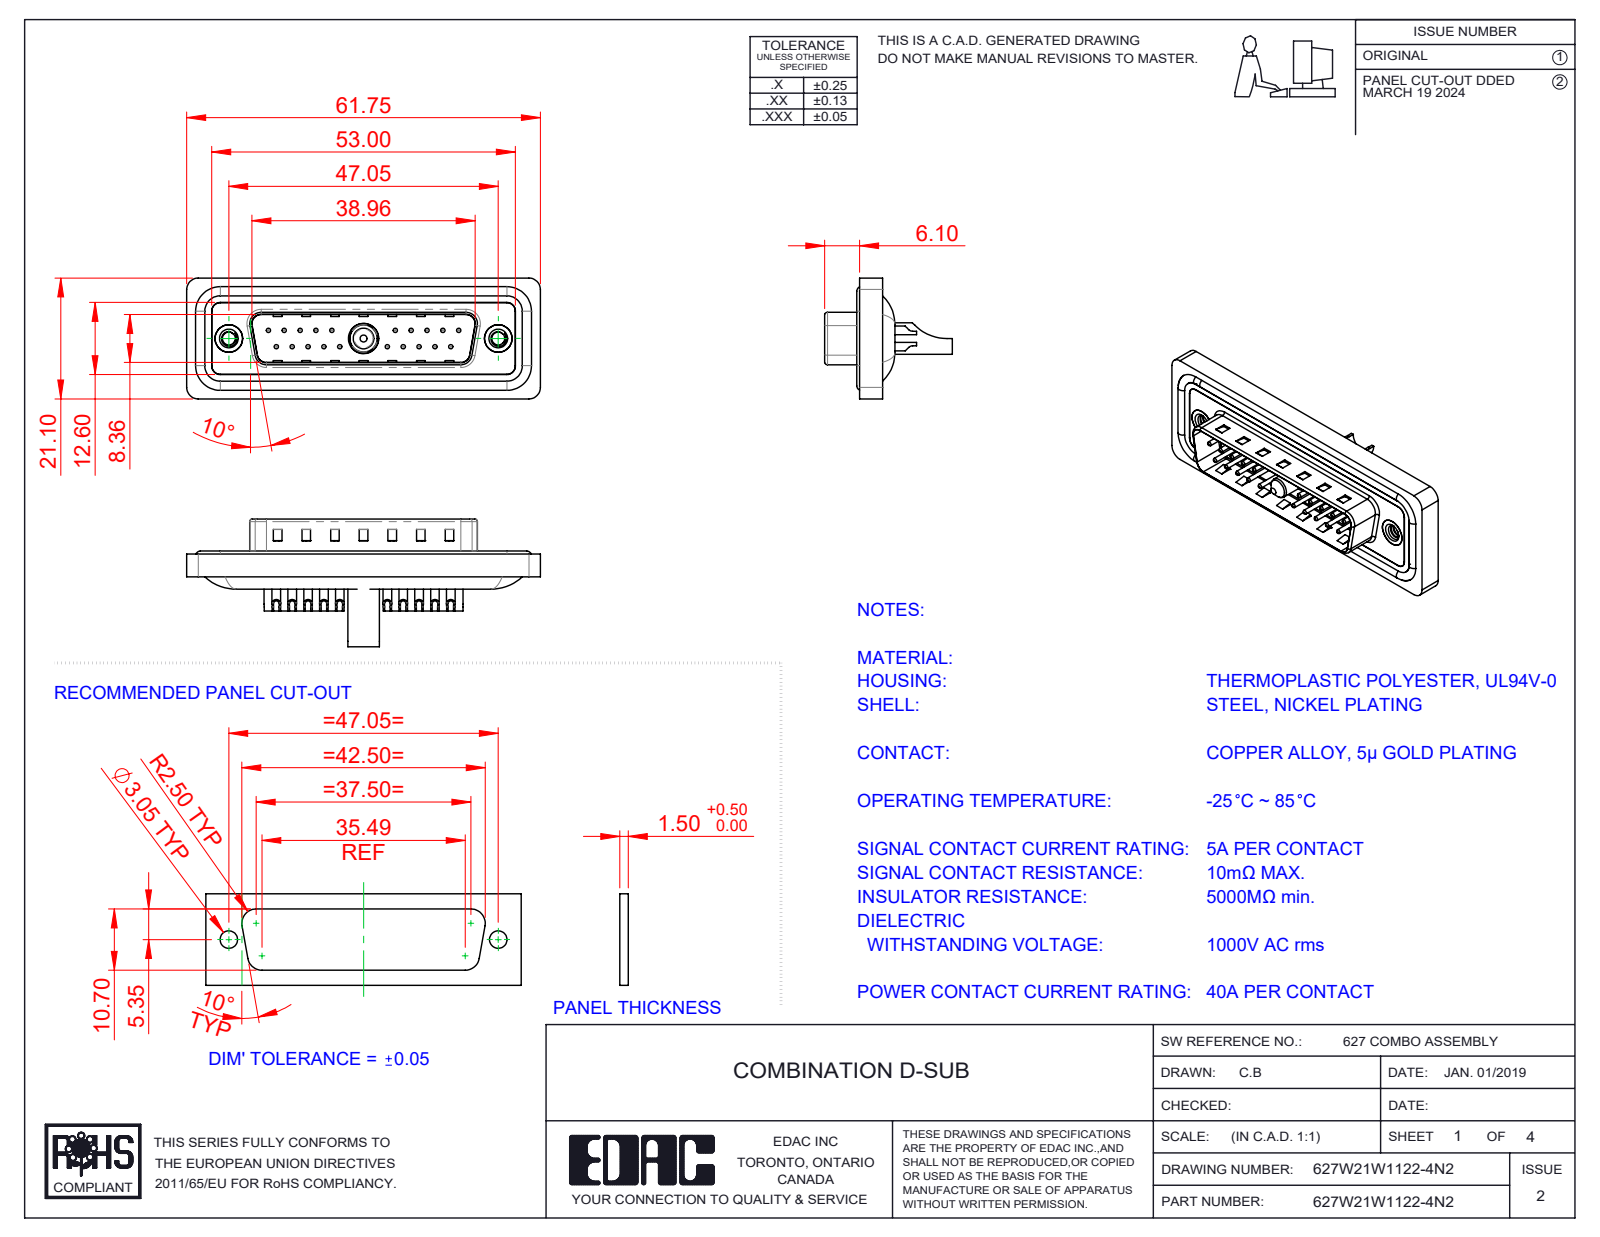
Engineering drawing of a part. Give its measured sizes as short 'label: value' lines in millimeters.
name: 627Combo Housing_21W1; 627Combo Threaded Rivet_2; 627Combo Shell Front_25 Contacts; Power Pin_40A SC (+5 more)
written by: SolidWorks 2023 (CONFIG_CONTROL_DESIGN)
unit: mm
bodies: 29 solids, 1265 faces (401 planar, 528 cylindrical, 336 other)
size: 61.75 × 22.3 × 21.1
volume: 7 268 mm³; area: 12 252 mm²
holes: 20× ⌀0.75, 20× ⌀1, 20× ⌀1.6, 20× ⌀2, 2× ⌀2.26, 2× ⌀4, 2× ⌀4.8, 2× ⌀5, 1× ⌀4.6, 1× ⌀4.85, 1× ⌀5.3
bosses: 20× ⌀1.5, 4× ⌀1.6, 2× ⌀4.9, 1× ⌀5.5, 1× ⌀5.2, 1× ⌀4.75, 1× ⌀3.75, 1× ⌀3.6
rounds: 22× R1.5, 18× R2, 8× R0.5, 8× R1.6, 6× R1, 4× R0.25, 4× R0.6, 4× R0.65
face distances: 0.4, 1.5, 1.1, 1.6, 0.5, 3.1, 2.9, 4.1, 0.82, 9.58
hole spacings: 3.16, 2.77, 5.54, 8.31, 5.04, 19.39, 20.97, 22.16
